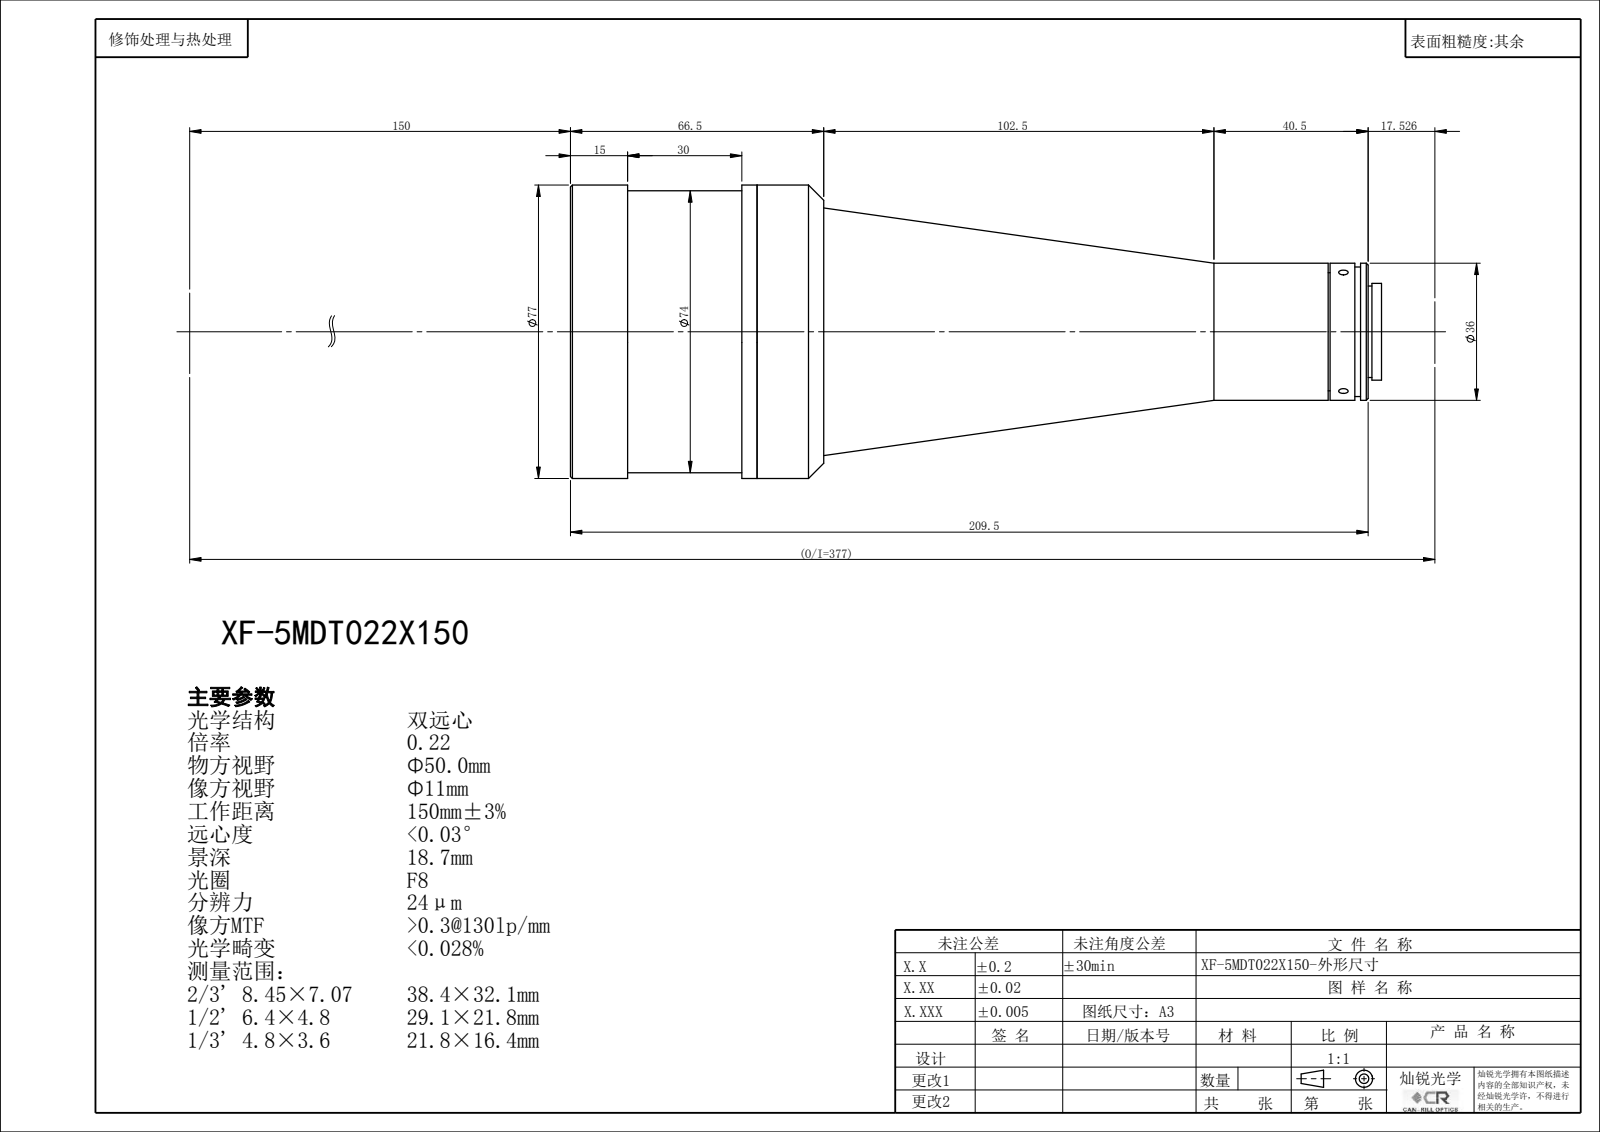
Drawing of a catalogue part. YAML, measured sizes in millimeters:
part_name: "XF-5MDT022X150"
step_written_by: "SolidWorks 2014 (CONFIG_CONTROL_DESIGN)"
units: millimeters
bodies: {solids: 0, faces: 93, planar: 35, cylindrical: 42, other: 16}
overall_size: [212.97, 77, 77]
round_holes:
  - {diameter: 2.5, count: 3}
  - {diameter: 16, count: 1}
  - {diameter: 19.4, count: 1}
  - {diameter: 21.4, count: 1}
  - {diameter: 63, count: 1}
  - {diameter: 65, count: 1}
  - {diameter: 70, count: 1}
round_bosses_or_shafts:
  - {diameter: 77, count: 1}
  - {diameter: 74, count: 1}
  - {diameter: 36, count: 1}
  - {diameter: 34, count: 1}
  - {diameter: 28, count: 1}
  - {diameter: 25.4, count: 1}
  - {diameter: 24, count: 1}
face_to_face_distances: [49, 207.47, 158.47, 209.47, 160.47, 2, 3.33, 45.67, 204.14, 206.14]
